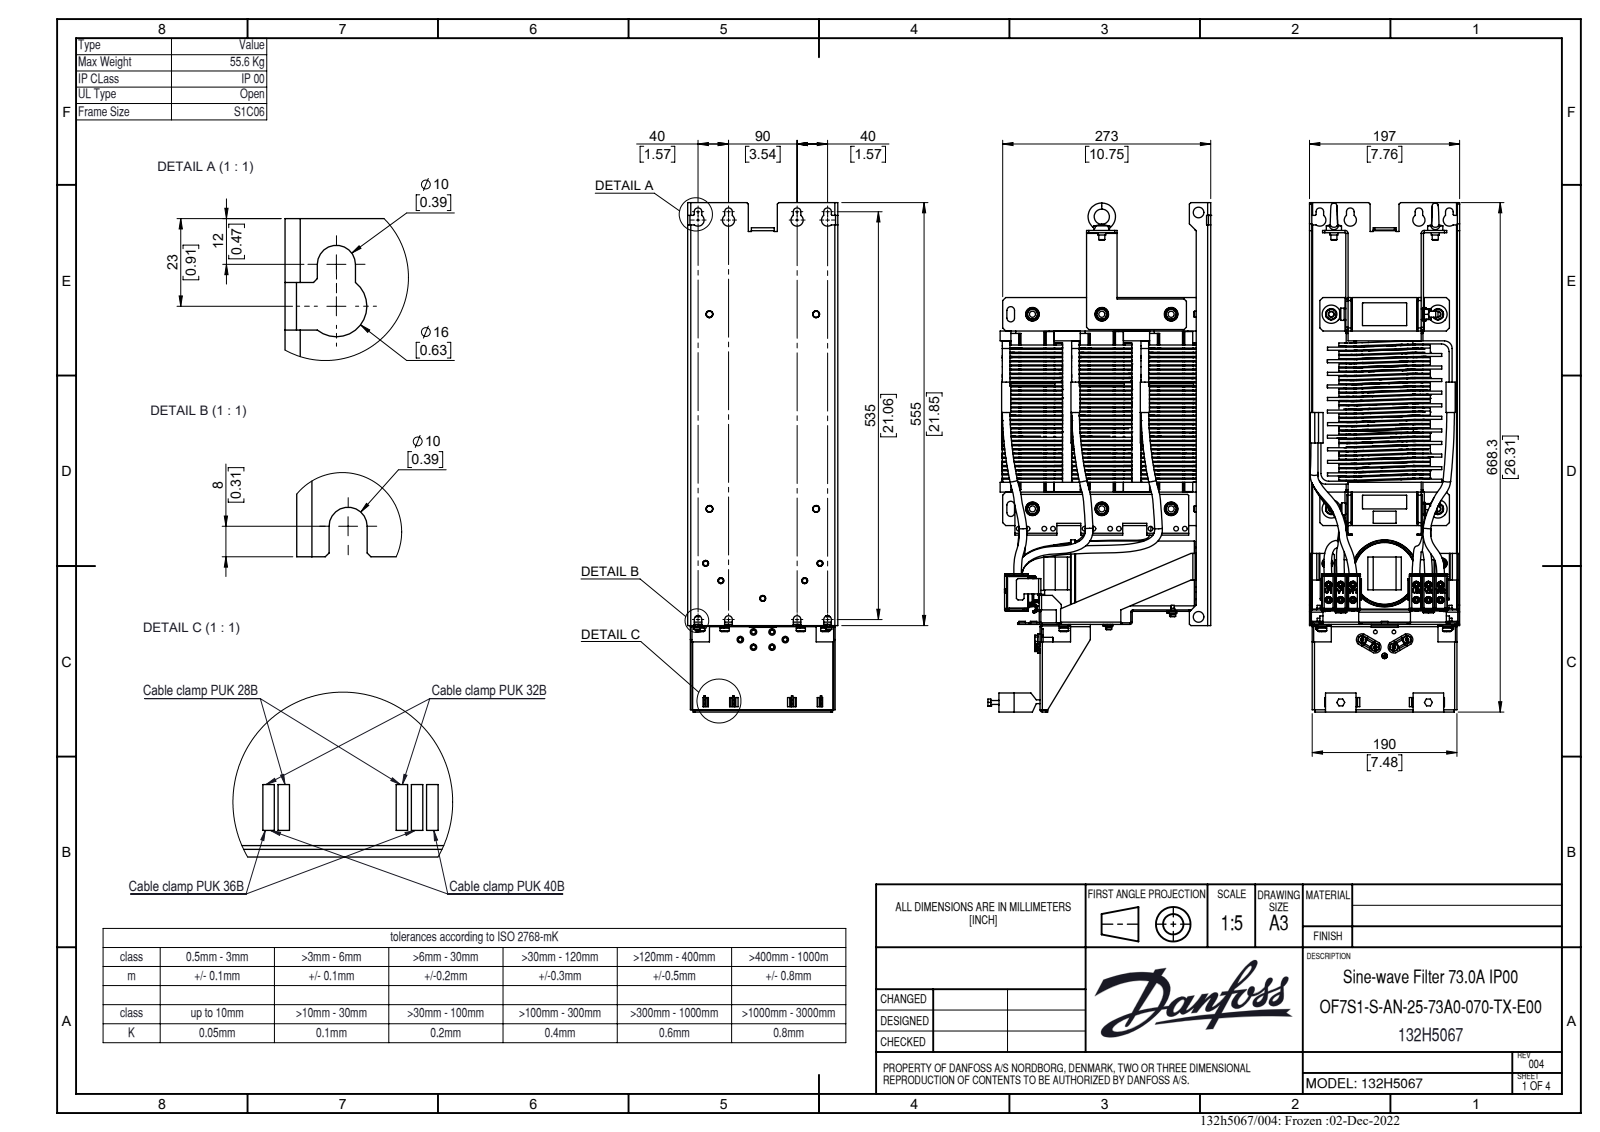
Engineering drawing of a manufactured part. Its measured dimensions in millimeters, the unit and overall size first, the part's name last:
Units: millimetres
Overall size (bounding box): 668.3 × 294.5 × 197
Round holes (diameter × count): ⌀6.2 ×16, ⌀8.02 ×11, ⌀5 ×6, ⌀7 ×5, ⌀4.2 ×4, ⌀4.5 ×4, ⌀8.4 ×4, ⌀6.5 ×3, ⌀6.8 ×2, ⌀14 ×2, ⌀6 ×1, ⌀7.15 ×1
Round bosses / shafts (diameter × count): ⌀8 ×21, ⌀6 ×14, ⌀8.5 ×7, ⌀16 ×5, ⌀24 ×4, ⌀15.01 ×4, ⌀11.55 ×4, ⌀8.9 ×4
Partial cylindrical surfaces — rounded edges, fillets, slot ends (radius × count): R1 ×43, R3 ×40, R0.5 ×12, R5 ×12, R5.5 ×12, R4.5 ×10, R4 ×7, R2.5 ×6
Main face-to-face distances: 3, 2, 1.5, 91, 5.5, 92, 255.3, 44, 7, 47.5
Hole centre spacings: 20, 18.03, 86.5, 10.05, 16, 25.61, 32.57, 115
Volume: 10 160 000 mm³ · Surface area: 1 193 000 mm²
Bodies: 10 solids, 2416 faces (1438 planar, 684 cylindrical, 294 other)
Part name (STEP PRODUCT): 132H5067-V002-050422_OUT
STEP written by: CREO PARAMETRIC BY PTC INC, 2020342 (CONFIG_CONTROL_DESIGN)
